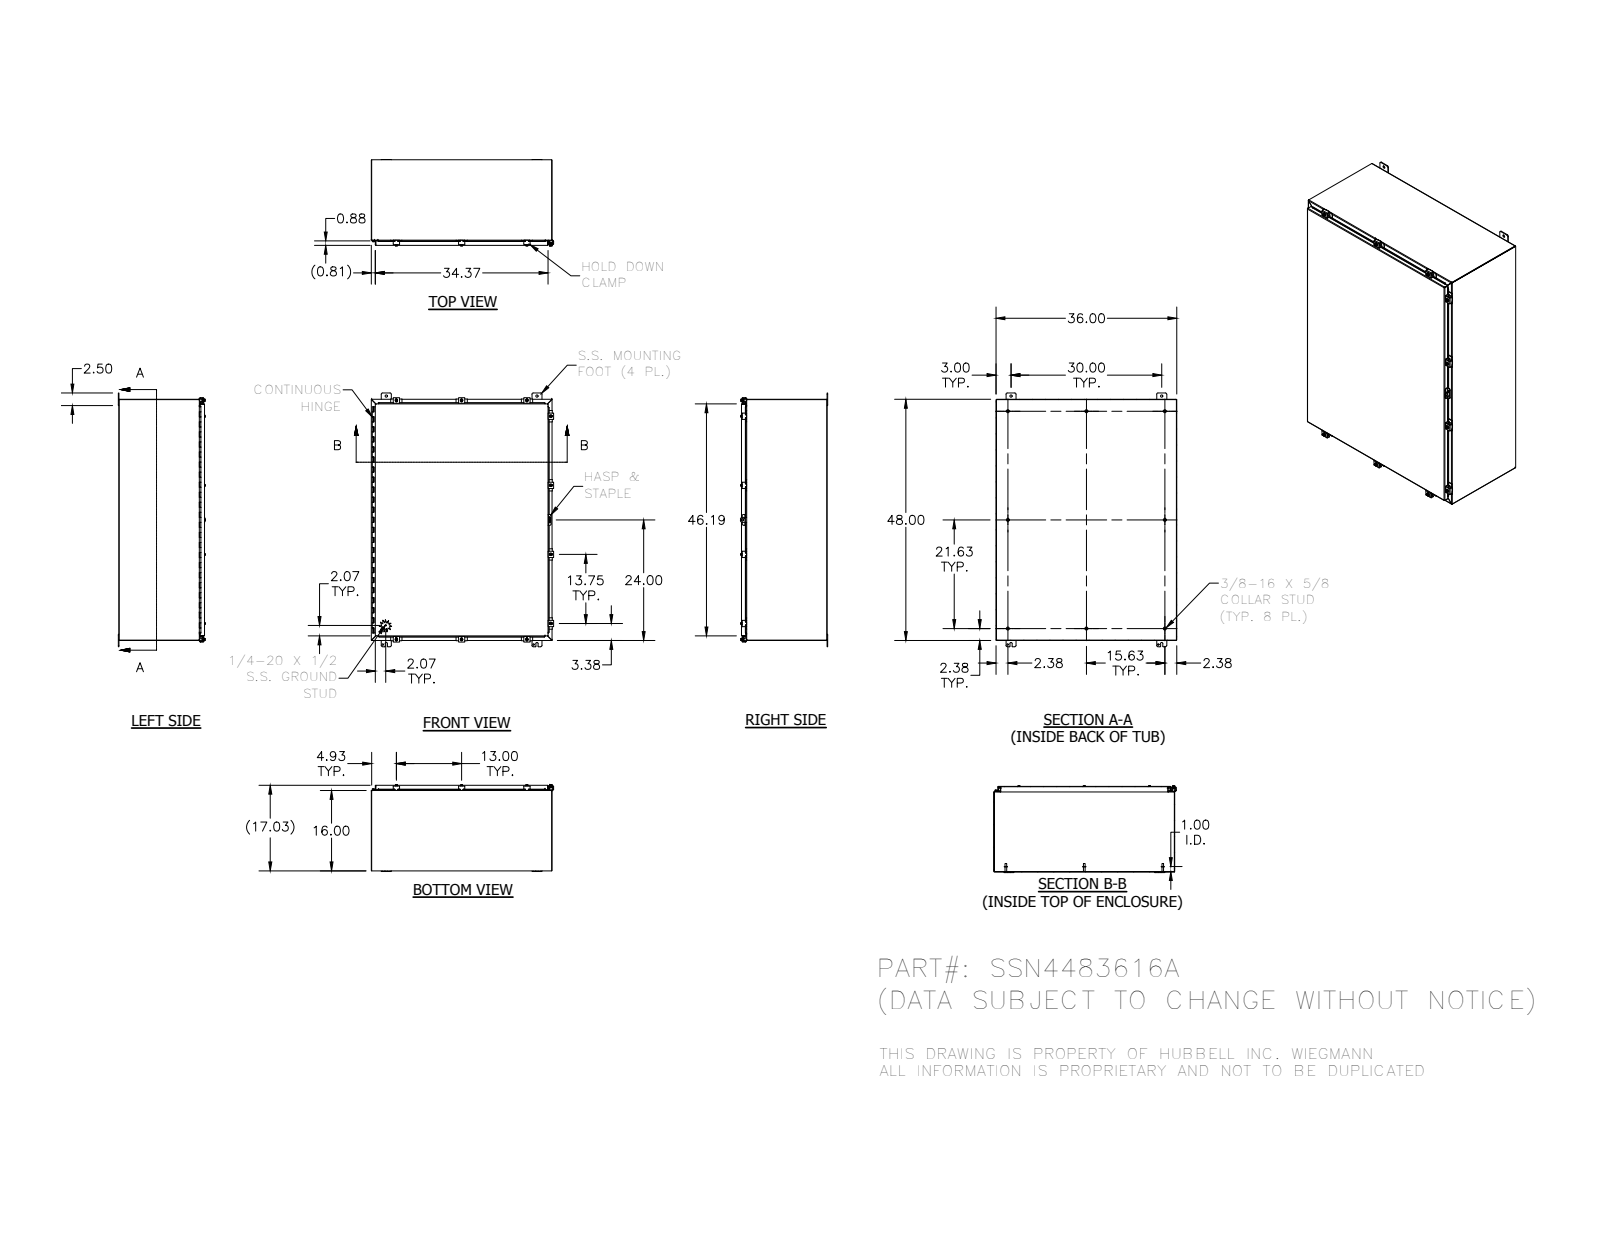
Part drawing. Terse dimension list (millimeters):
name: 38846; 30819; 32874-48L; SSN4483616A (+8 more)
written by: SolidWorks 2014 (AUTOMOTIVE_DESIGN)
unit: mm
bodies: 73 solids, 2680 faces (1093 planar, 1174 cylindrical, 413 other)
size: 1282.7 × 922.3 × 440.8
volume: 8 398 000 mm³; area: 8 795 000 mm²
holes: 10× ⌀5.4, 10× ⌀7.1, 10× ⌀7.6, 4× ⌀8, 4× ⌀11.1, 1× ⌀3.2, 1× ⌀4, 1× ⌀12.7
bosses: 12× ⌀6.4, 10× ⌀13.2, 10× ⌀12.7, 10× ⌀8.9, 8× ⌀15.9, 8× ⌀8.4, 1× ⌀8.6, 1× ⌀3
rounds: 117× R0.8, 41× R3.2, 37× R6.4, 21× R0.8, 21× R2.7, 20× R3.6, 18× R1.6, 14× R2.5
face distances: 1.9, 430.8, 428.9, 432.6, 912.5, 1217.3, 910.6, 914.4, 1215.4, 1219.2
hole spacings: 349.3, 40.5, 330.2, 459.5, 698.5, 762, 786.7, 1219.2
